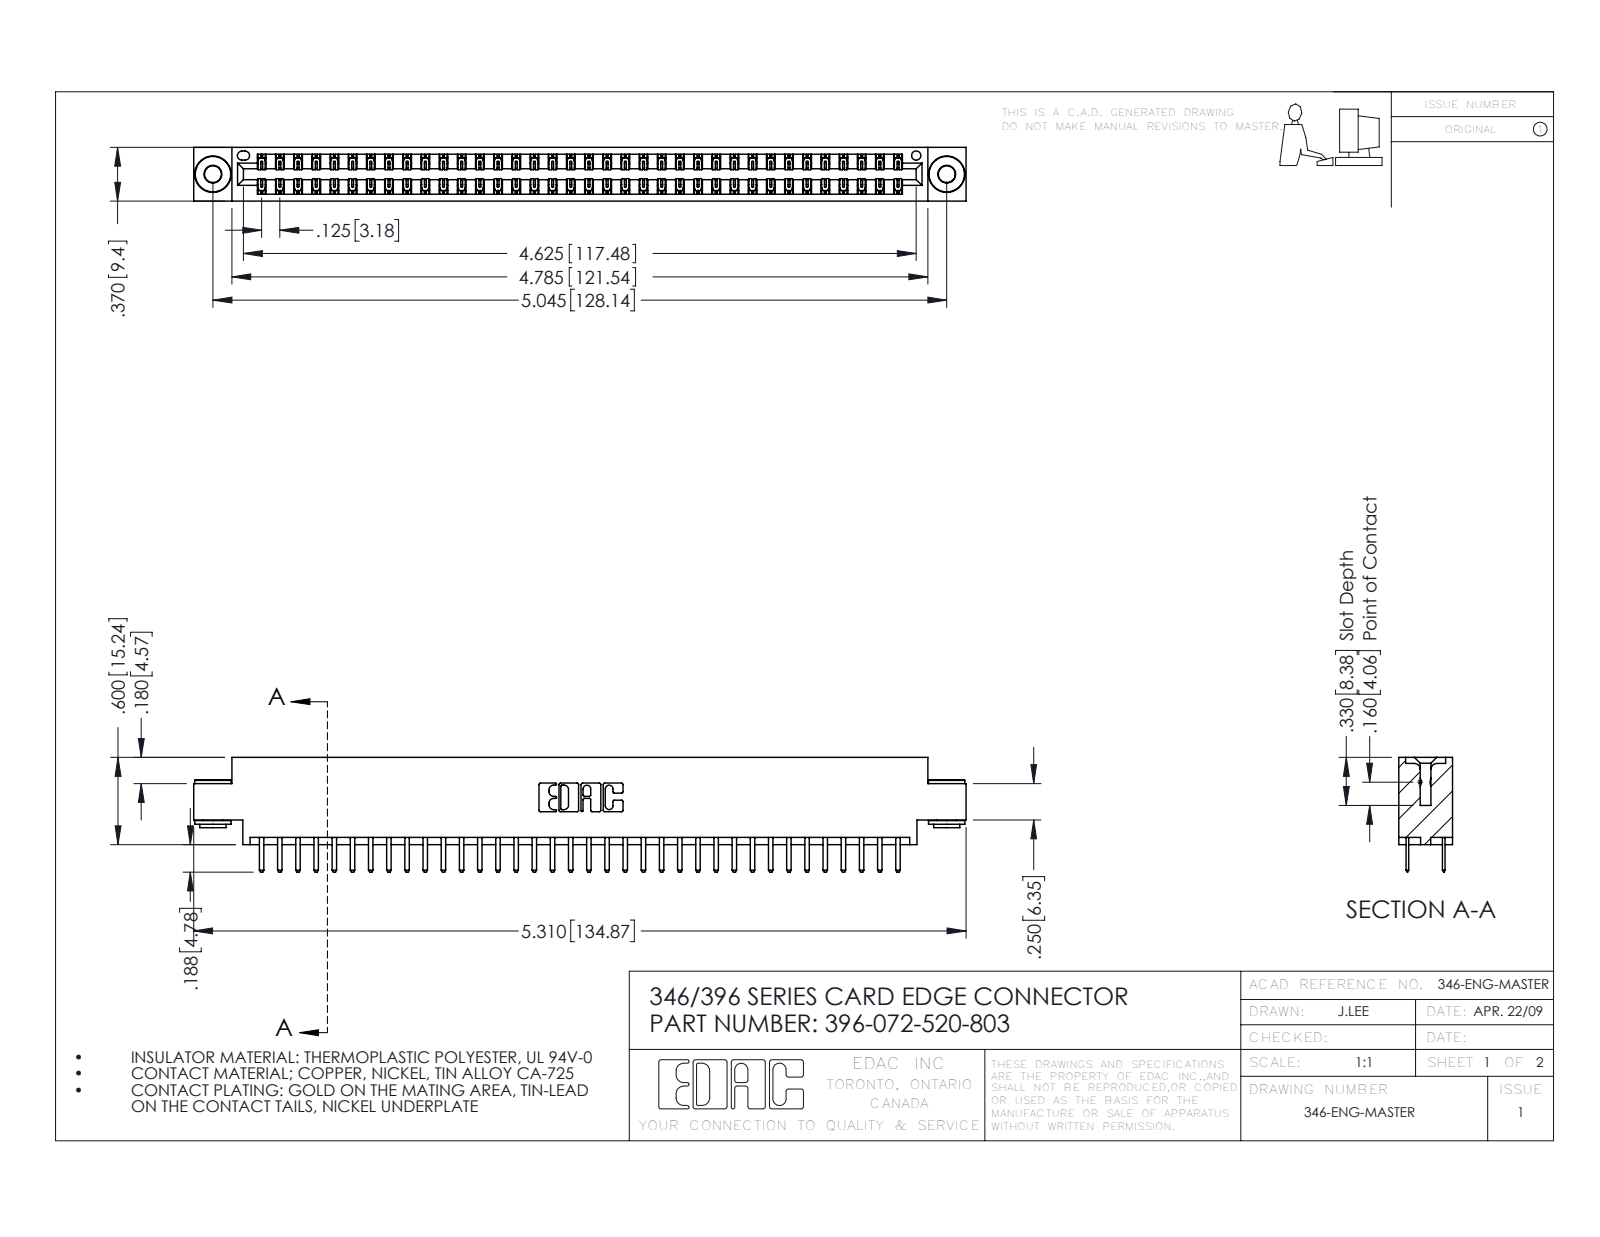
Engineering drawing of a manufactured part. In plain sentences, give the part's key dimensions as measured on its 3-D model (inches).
The part is named "345-250-002_345-250-002-102; 346 Part_0.170 Offset - 0.156 Dia-TH; 396-072-520-803; 345-292-001_345-293-120". Its 3-D file was written by "SolidWorks 2016 (CONFIG_CONTROL_DESIGN)". It is 75 solids with 4196 faces: 2754 planar, 1434 cylindrical and 8 other. Overall it measures 5.31 by 0.788 by 0.37 inches. Its volume is 0.79 cubic inches and its surface area 27.92 square inches. Round holes: 2 of diameter 0.116, 2 of diameter 0.156, 1 of diameter 0.064. Round bosses or shafts: 2 of diameter 0.25, 2 of diameter 0.18, 2 of diameter 0.136. Partial cylindrical surfaces (rounded edges, fillets, slot ends): 108 of radius 0.006, 76 of radius 0.01, 22 of radius 0.01, 6 of radius 0.007, 6 of radius 0.031, 3 of radius 0.026, 2 of radius 0.014, 2 of radius 0.022. The main face-to-face distances are 0.048, 0.322, 0.37, 0.25, 0.025, 0.275, 0.072, 0.298, 0.148, 0.222. The hole center spacings are 0.246, 4.836, 5.045.
